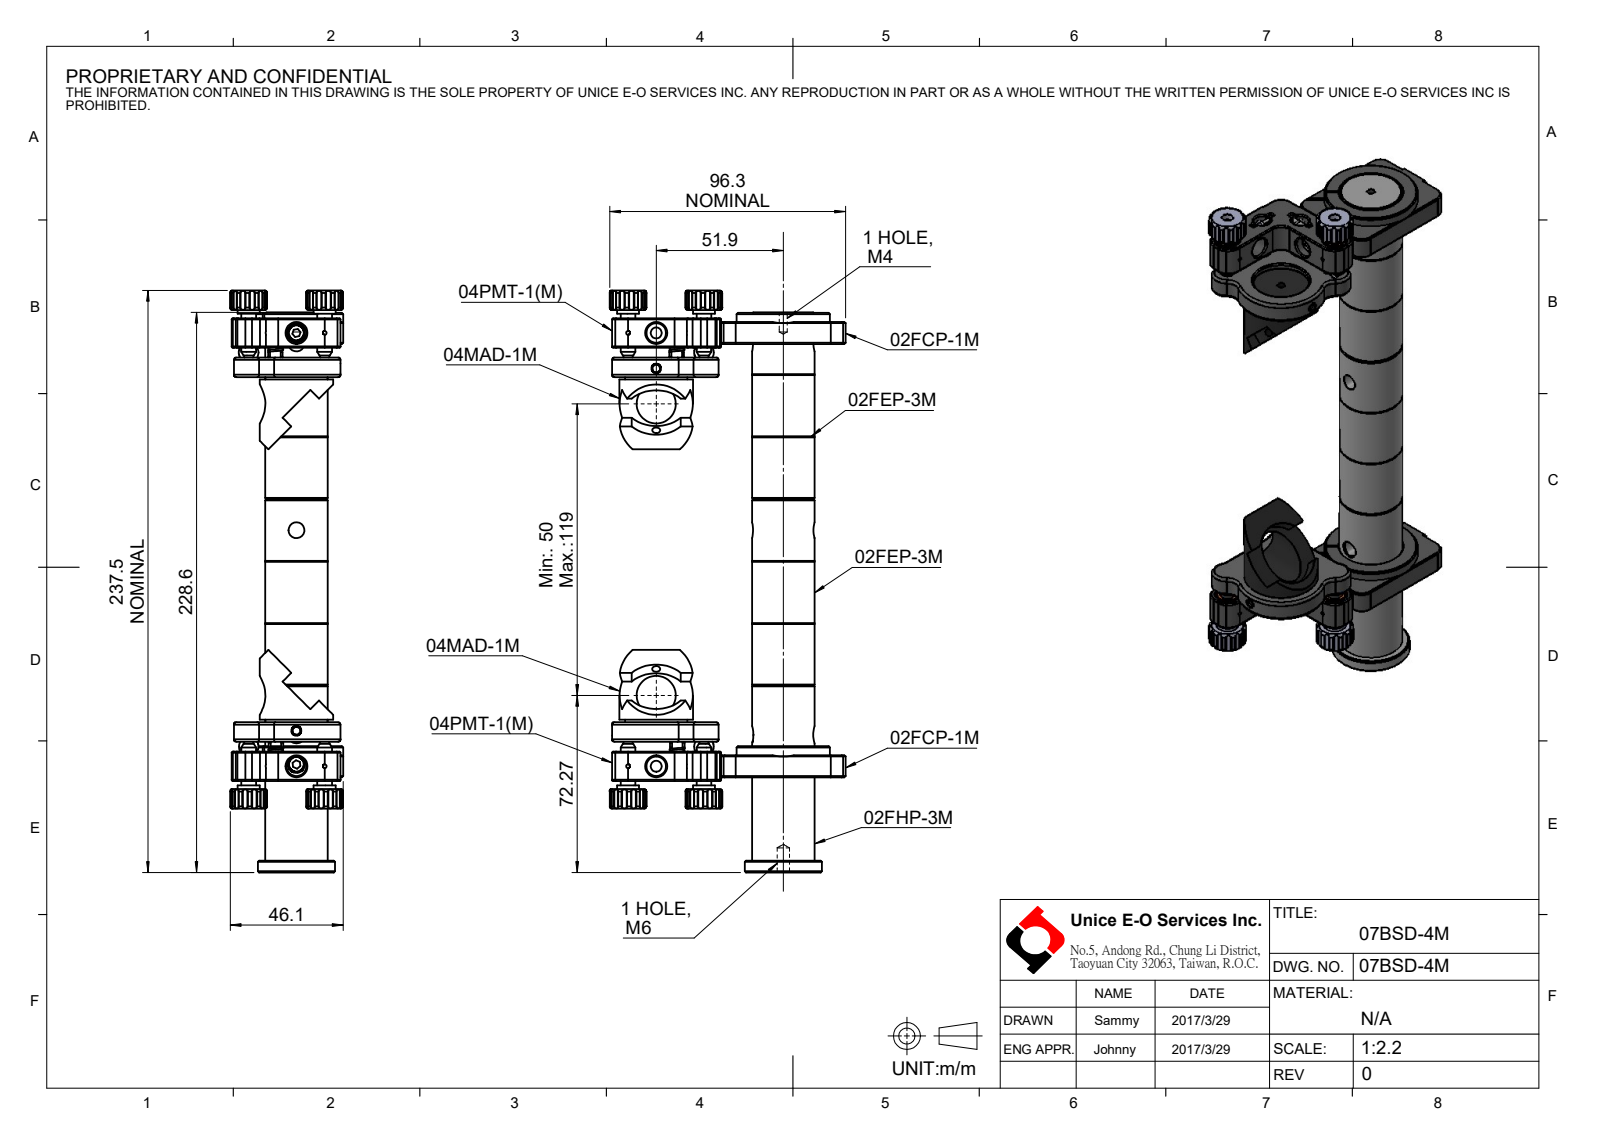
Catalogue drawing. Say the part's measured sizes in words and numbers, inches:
The part is named "07BSD-4M". Its 3-D file was written by "SolidWorks 2016 (CONFIG_CONTROL_DESIGN)". It is 57 solids with 1665 faces: 393 planar, 768 cylindrical and 504 other. Overall it measures 9.352 by 3.791 by 1.813 inches. Its volume is 12.53 cubic inches and its surface area 120.1 square inches. Round holes: 10 of diameter 0.13, 8 of diameter 0.039, 6 of diameter 0.177, 6 of diameter 0.315, 4 of diameter 0.063, 4 of diameter 0.067, 3 of diameter 0.197, 3 of diameter 0.256, 2 of diameter 0.157, 2 of diameter 0.185, 2 of diameter 0.232, 2 of diameter 0.236. Round bosses or shafts: 32 of diameter 0.031, 12 of diameter 0.059, 6 of diameter 0.157, 4 of diameter 0.276, 2 of diameter 0.354, 2 of diameter 0.098, 1 of diameter 1.5, 1 of diameter 1.24. Partial cylindrical surfaces (rounded edges, fillets, slot ends): 96 of radius 0.012, 50 of radius 0.059, 40 of radius 0.02, 23 of radius 0.197, 12 of radius 0.039, 9 of radius 0.098, 8 of radius 0.03, 3 of radius 0.236. The main face-to-face distances are 6.963, 0.315, 0.472, 0.059, 0.217, 6.077, 0.413, 6.491, 0.531, 5.861. The hole center spacings are 6.963, 0.453, 0.679, 0.984, 6.381, 6.421, 6.978, 0.335.
